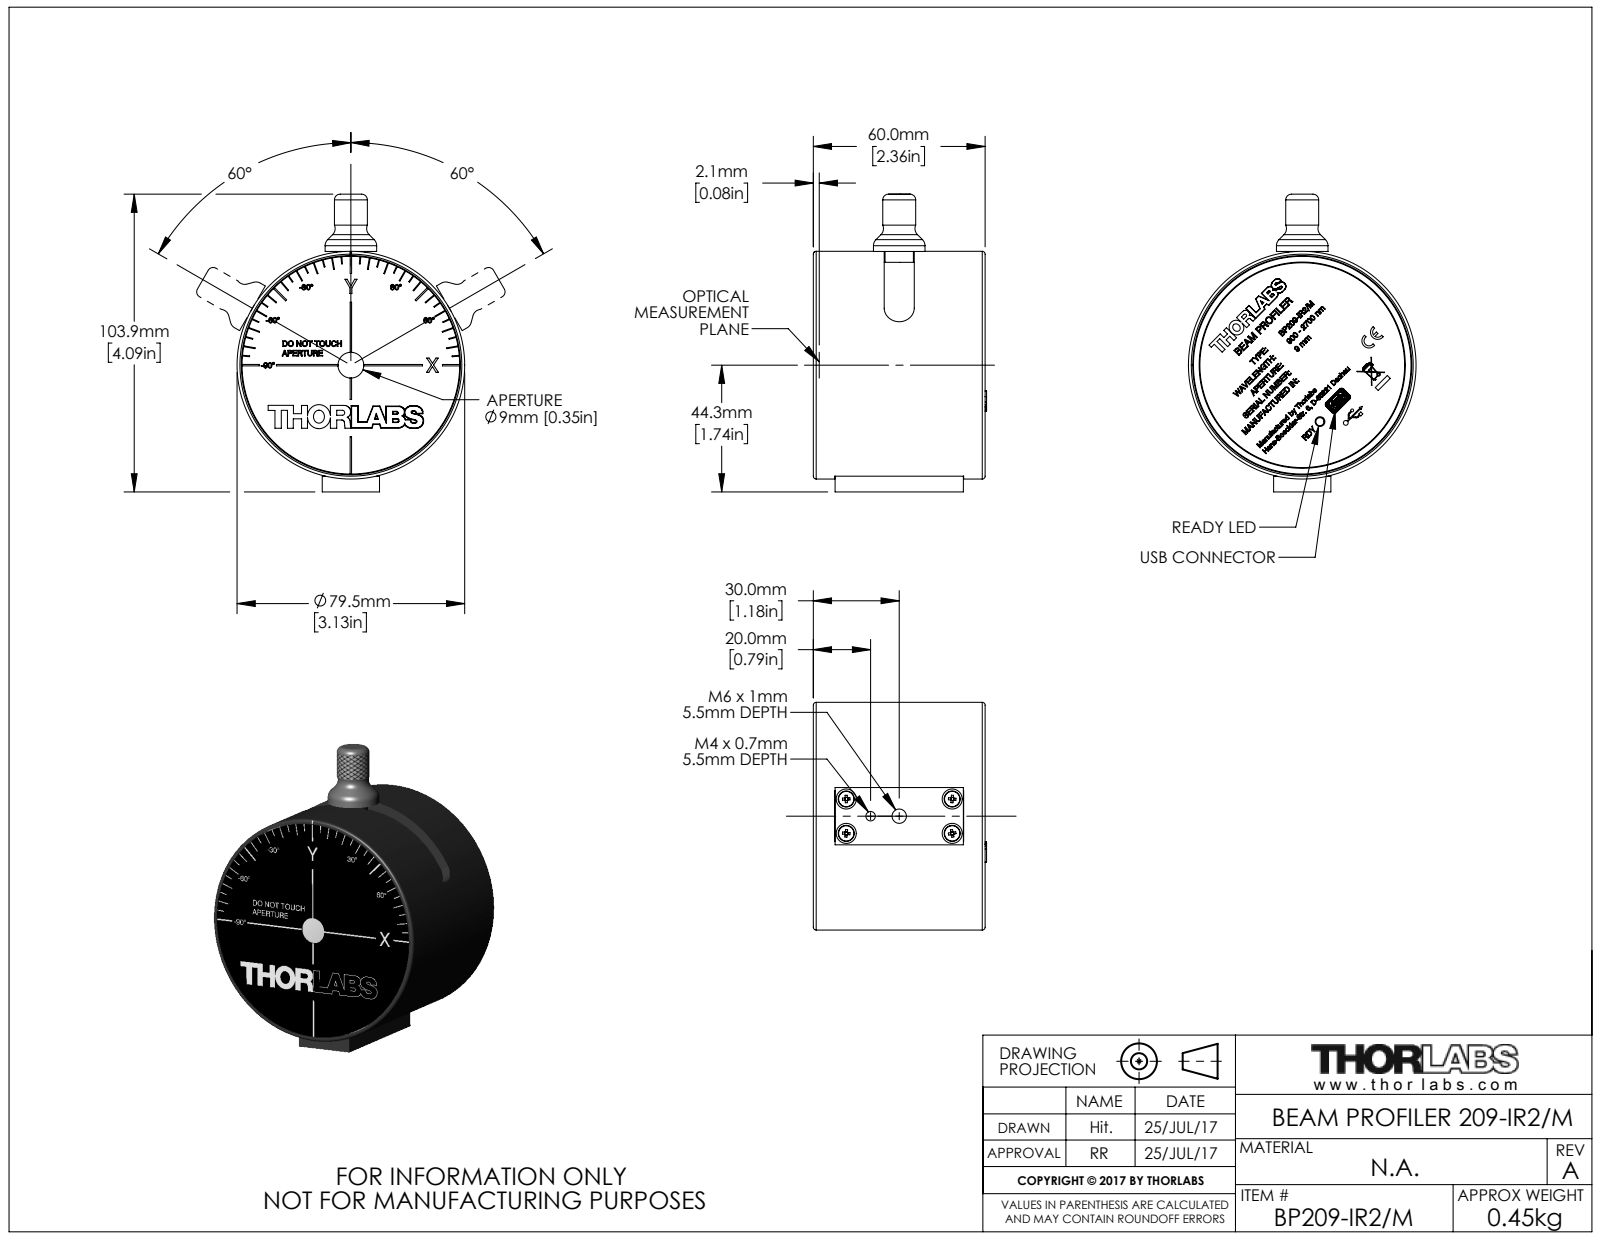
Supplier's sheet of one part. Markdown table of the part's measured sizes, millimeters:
| quantity | value |
| --- | --- |
| part name | MTN004189-E0W |
| STEP written by | SolidWorks 2016 (AUTOMOTIVE_DESIGN) |
| units | millimeters |
| bodies | 14 solids, 4826 faces (3261 planar, 408 cylindrical, 1157 other) |
| overall size | 103.95 × 79.5 × 60.5 |
| volume | 98 412 mm³ |
| surface area | 99 234 mm² |
| round holes (diameter × count) | 3.2 × 10, 2.2 × 9, 8 × 8, 1.6 × 6, 6.3 × 6, 5 × 5, 7 × 5, 2.5 × 4, 5.3 × 4, 1 × 1, 1.29 × 1, 1.67 × 1 |
| round bosses / shafts (diameter × count) | 5.6 × 4, 3 × 4, 0.8 × 2, 79.5 × 1, 76 × 1, 72.1 × 1, 71.8 × 1, 71.5 × 1 |
| partial cylindrical surfaces (radius × count) | 1.5 × 18, 4 × 16, 0.1 × 14, 0.2 × 14, 1 × 14, 0.3 × 9, 0.7 × 8, 5 × 8 |
| main face-to-face distances | 1, 59, 59.7, 60, 58, 0.7, 58.7, 0.5, 2, 1.5 |
| hole center spacings | 23.73, 31, 43.84, 57.28, 27, 46.77, 27.01, 19.45 |
